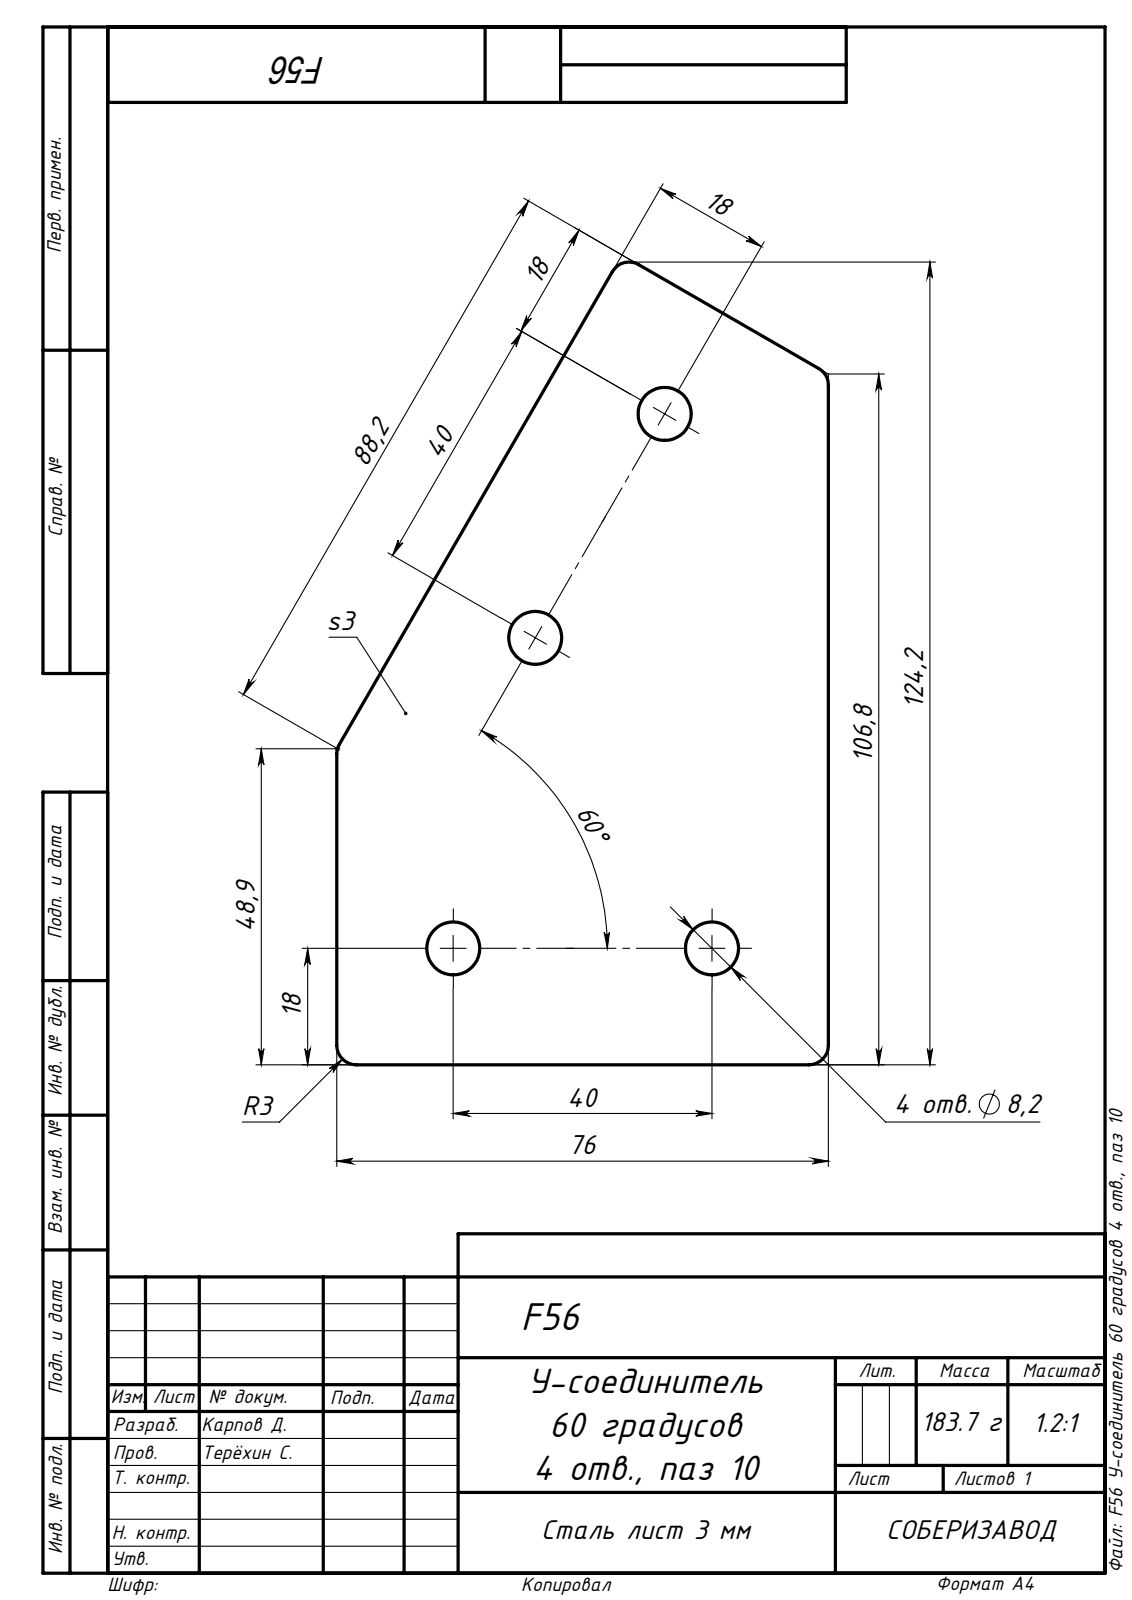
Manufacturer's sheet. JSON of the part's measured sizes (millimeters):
{"part_name": "F56 У-соединитель 60 градусов 4 отв., паз 10_00; F56 У-соединитель 60 градусов 4 отв., паз 10", "step_written_by": "SolidWorks 2025 (CONFIG_CONTROL_DESIGN)", "units": "millimeters", "bodies": {"solids": 1, "faces": 20, "planar": 7, "cylindrical": 13, "other": 0}, "overall_size": [131.17, 76, 3], "volume_mm3": 23572, "surface_area_mm2": 17123, "round_holes": [[8.2, 4]], "partial_cylinders_radius": [[3, 5]], "face_to_face_distances": [3, 76], "hole_center_spacings": [40, 56.48, 61.45, 89.98, 95.45]}
